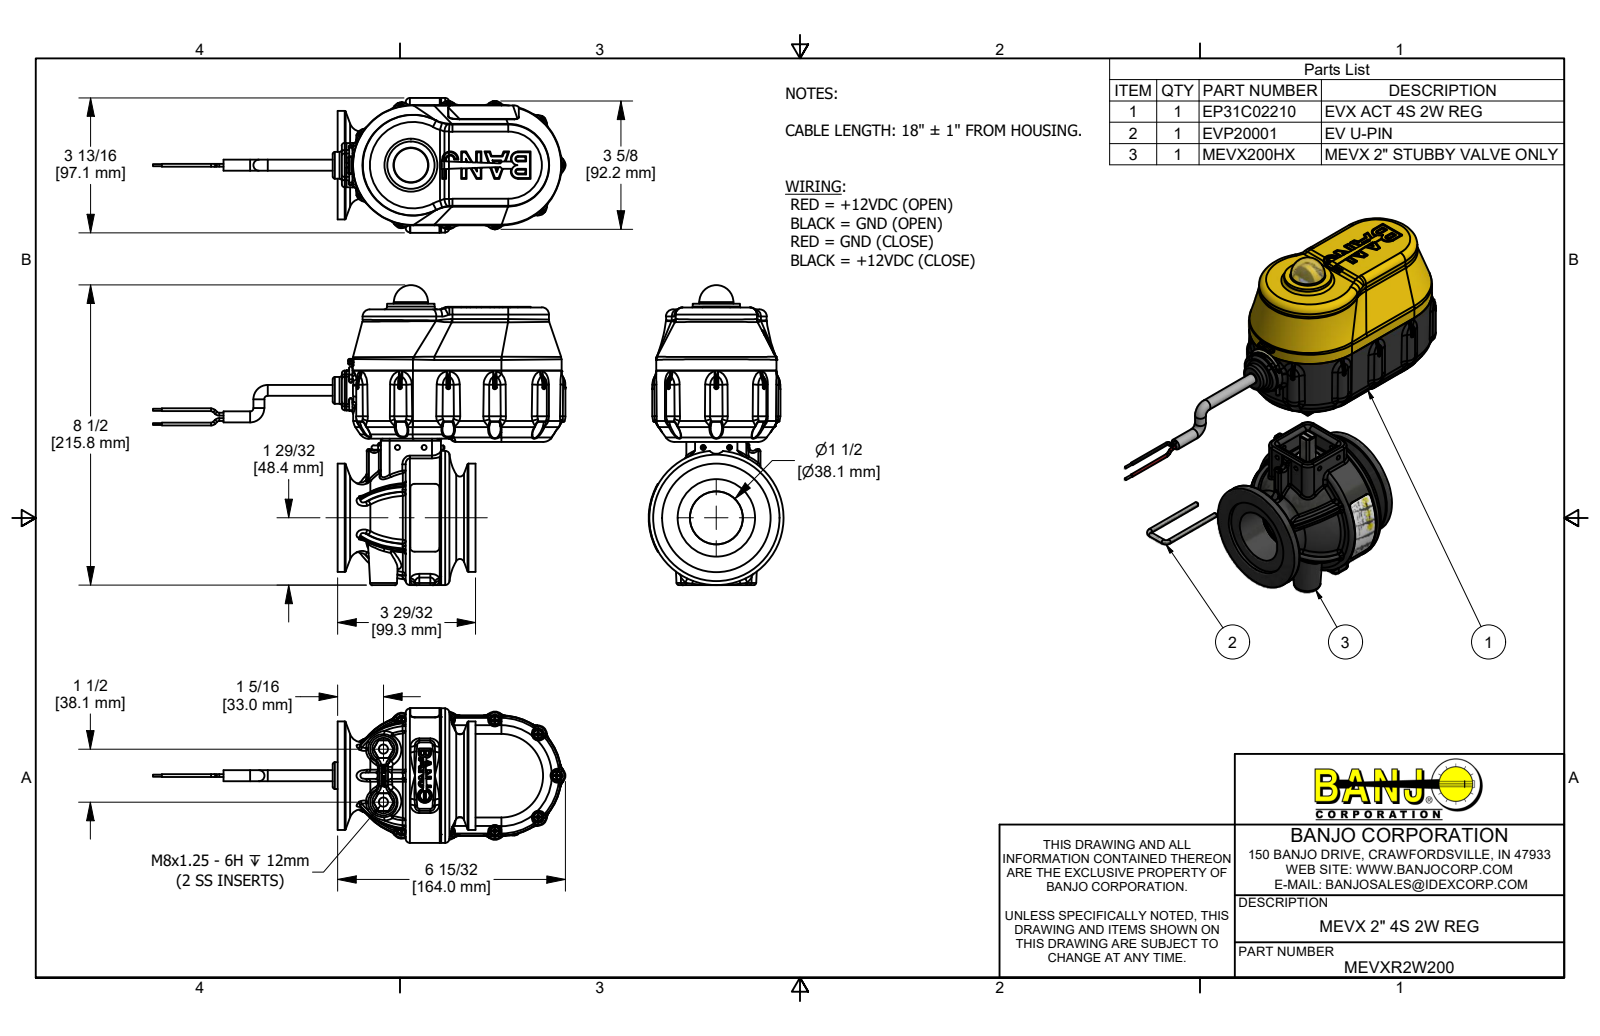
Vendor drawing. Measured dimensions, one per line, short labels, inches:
name: MEVXR2W200; EP31C02210; 91400A119; 95584A200 (+8 more)
written by: Autodesk Inventor 2019 (AUTOMOTIVE_DESIGN)
unit: in
bodies: 83 solids, 12219 faces (3698 planar, 3068 cylindrical, 5453 other)
size: 11.685 × 8.497 × 3.823
volume: 51.19 in³; area: 573.2 in²
holes: 13× ⌀0.15, 11× ⌀0.095, 5× ⌀0.135, 4× ⌀0.107, 4× ⌀0.126, 4× ⌀0.136, 4× ⌀0.17, 2× ⌀0.089, 2× ⌀0.105, 2× ⌀0.115, 2× ⌀0.118, 2× ⌀0.123
bosses: 17× ⌀0.25, 11× ⌀0.14, 11× ⌀0.108, 11× ⌀0.085, 10× ⌀0.08, 4× ⌀0.27, 4× ⌀0.219, 4× ⌀0.164
rounds: 147× R0.04, 83× R0.02, 56× R0.01, 47× R0.06, 43× R0.005, 28× R0.08, 26× R0.03, 26× R0.125
face distances: 0.1, 2.565, 0.945, 1.685, 0.78, 2.465, 0.88, 0.035, 0.987, 3.005
hole spacings: 2.023, 1.283, 1.662, 2.73, 2.967, 3.45, 0.487, 0.492
